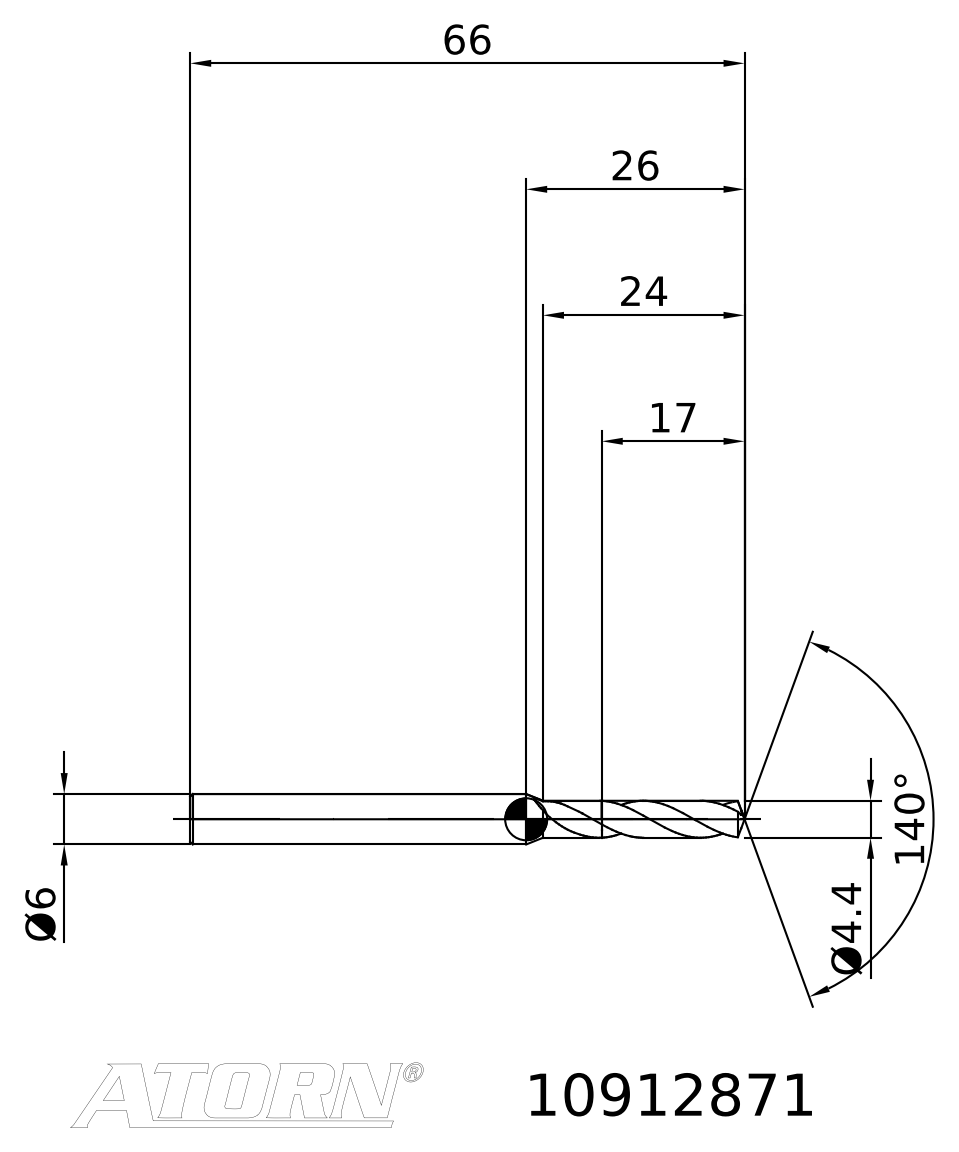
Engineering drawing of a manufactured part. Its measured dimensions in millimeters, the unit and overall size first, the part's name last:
Units: millimetres
Overall size (bounding box): 66 × 6.91 × 6
Main face-to-face distances: 49
Volume: 1 412 mm³ · Surface area: 1 197 mm²
Bodies: 2 solids, 25 faces (3 planar, 0 cylindrical, 22 other)
STEP written by: TDM (AUTOMOTIVE_DESIGN)
